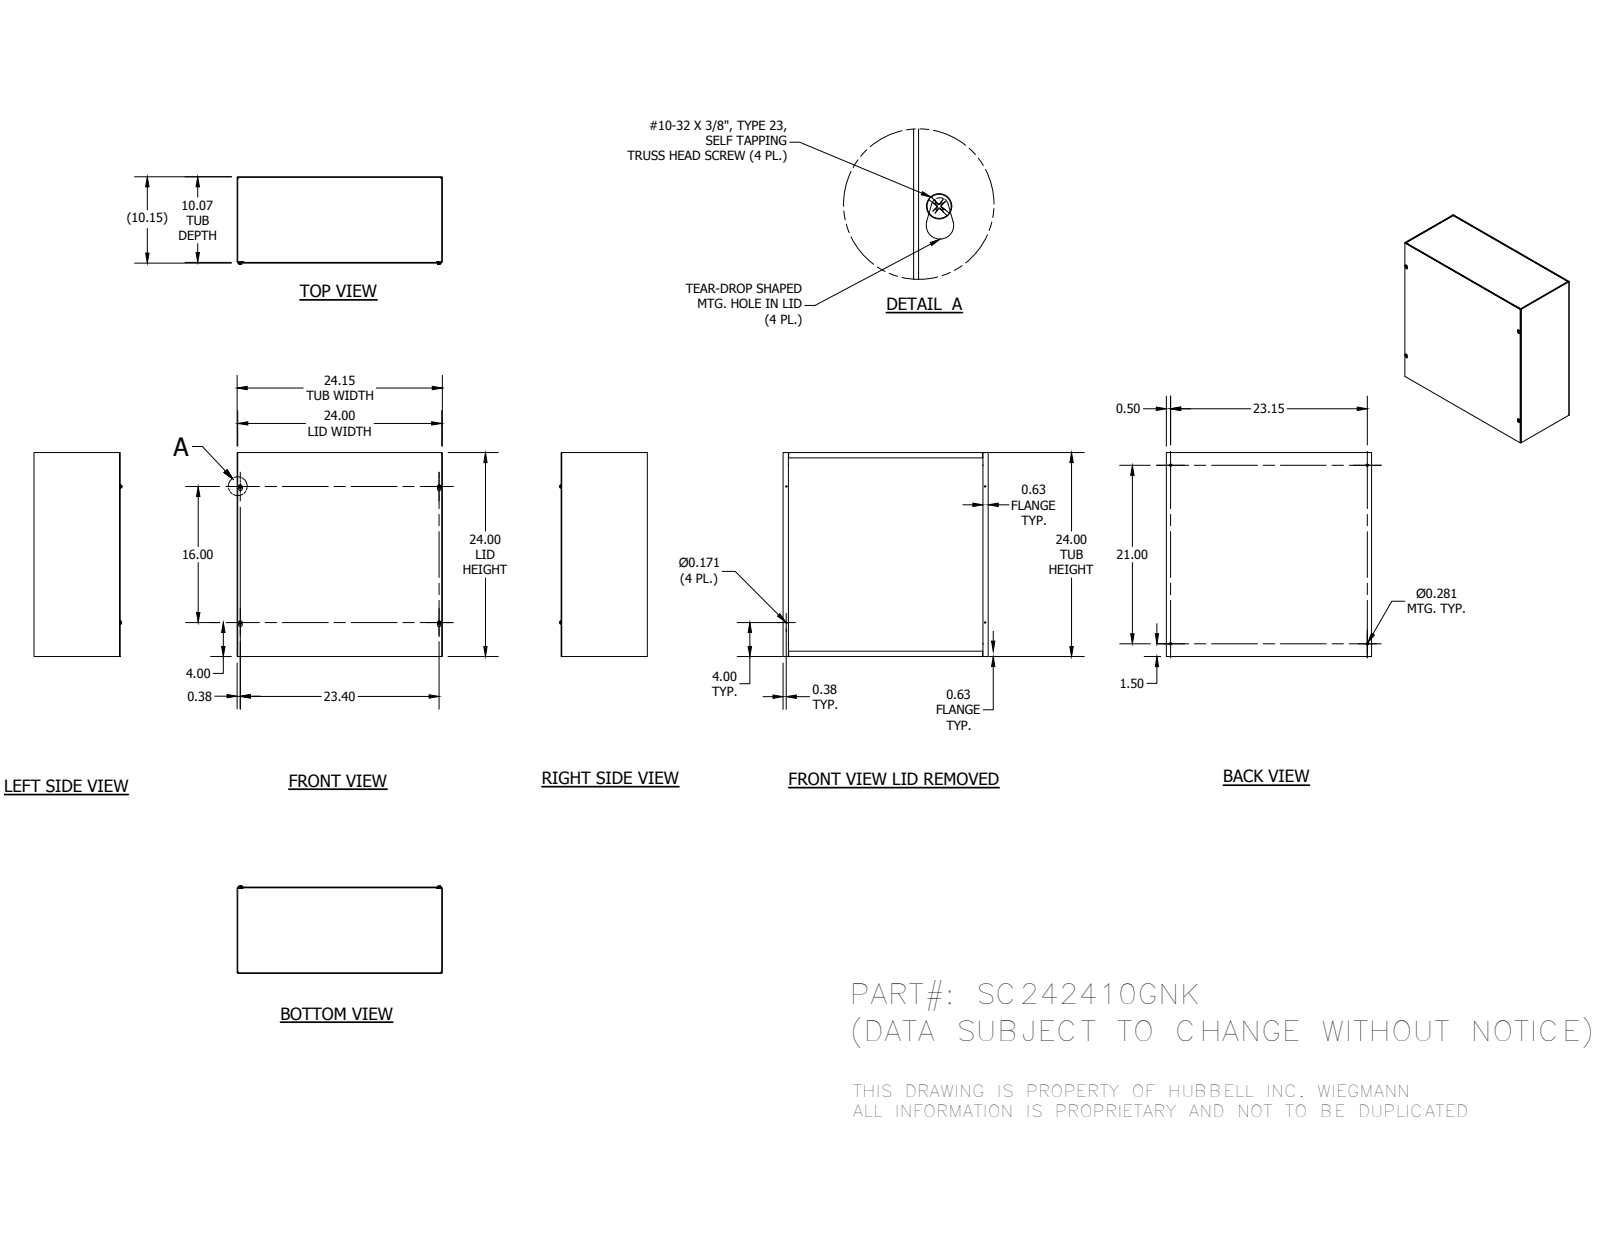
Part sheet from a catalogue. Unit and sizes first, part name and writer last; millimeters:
Units: millimetres
Overall size (bounding box): 613.36 × 609.6 × 261.11
Round holes (diameter × count): ⌀4.34 ×4, ⌀7.14 ×4
Round bosses / shafts (diameter × count): ⌀4.83 ×4
Partial cylindrical surfaces — rounded edges, fillets, slot ends (radius × count): R0.4 ×12, R2.28 ×12, R3.17 ×4, R5.16 ×4
Main face-to-face distances: 1.88, 255.88, 254, 257.76, 609.6, 607.72, 611.48, 605.84, 613.36, 3.76
Hole centre spacings: 63.58, 469.91, 594.53, 755.14, 406.4, 533.4, 587.96, 594.3
Volume: 2 680 000 mm³ · Surface area: 2 870 000 mm²
Bodies: 8 solids, 320 faces (192 planar, 44 cylindrical, 84 other)
Part name (STEP PRODUCT): SC242410GNKBLR; SC2410GNKTB; SC2424GLPA; 37214 (+1 more)
STEP written by: Autodesk Inventor 2014 (AUTOMOTIVE_DESIGN)
